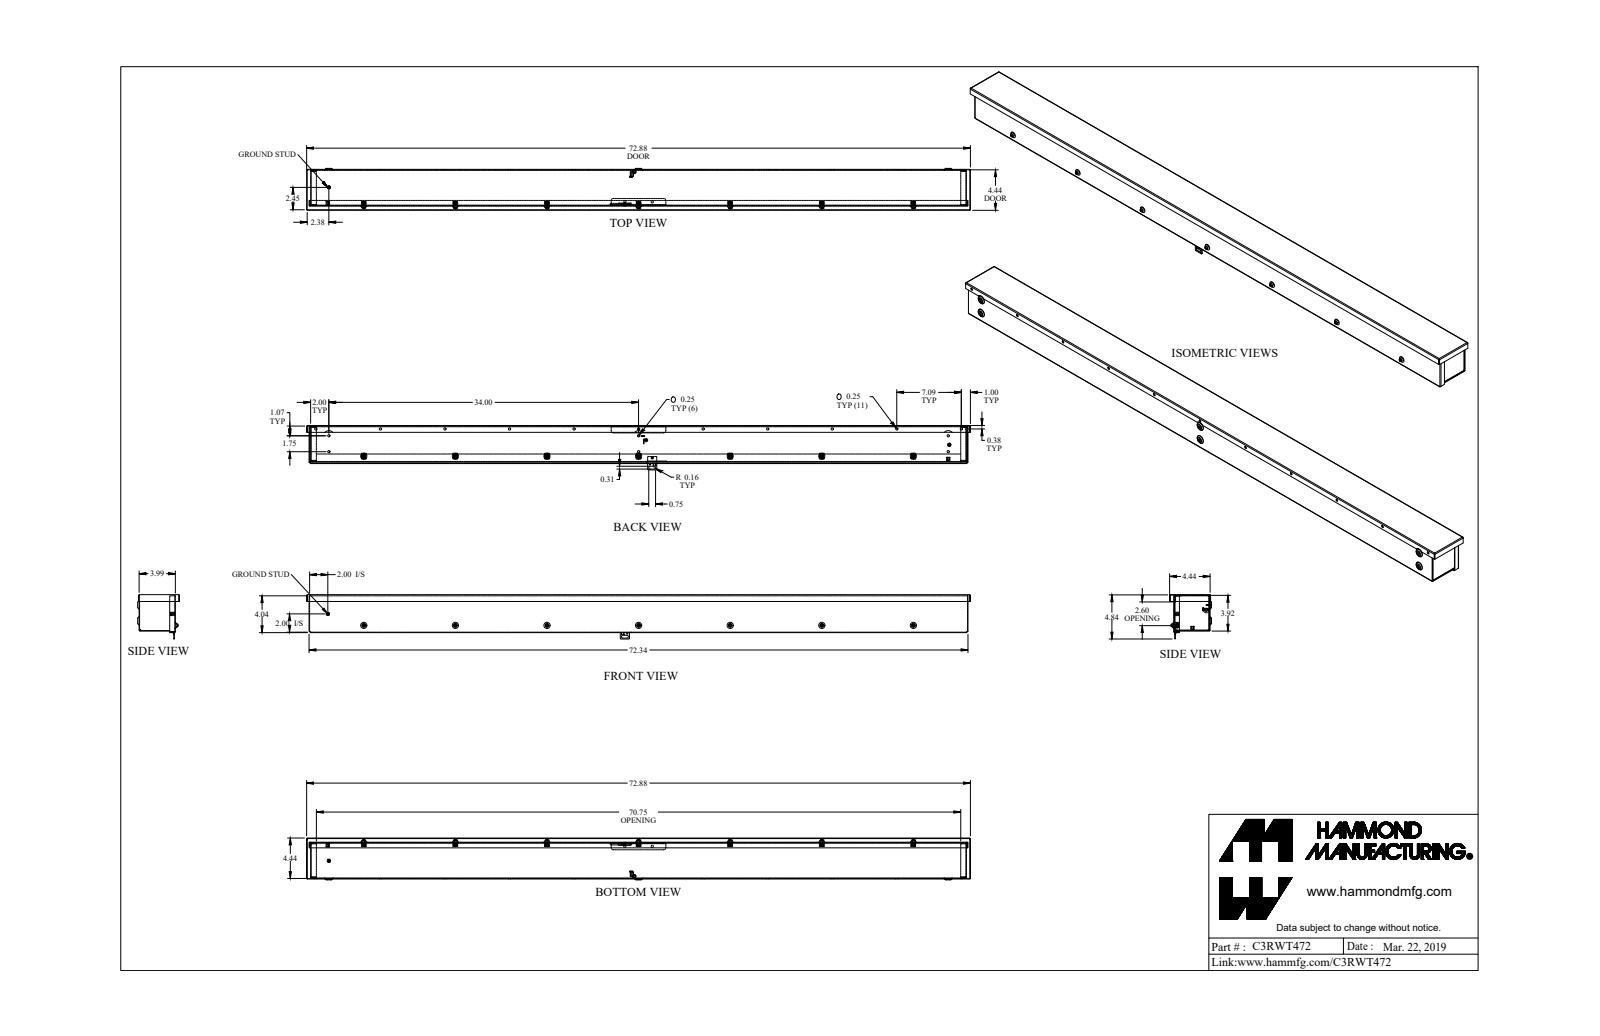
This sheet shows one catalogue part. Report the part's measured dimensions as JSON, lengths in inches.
{"part_name": "C3RWT472_Default", "step_written_by": "SolidWorks 2019 (CONFIG_CONTROL_DESIGN)", "units": "inches", "bodies": {"solids": 35, "faces": 1323, "planar": 712, "cylindrical": 423, "other": 188}, "overall_size": [72.875, 4.871, 4.594], "volume_in3": 82.77, "surface_area_in2": 2939, "round_holes": [[0.25, 19], [0.156, 9], [0.214, 7], [0.23, 7], [0.203, 2], [0.125, 1], [0.137, 1], [0.2, 1], [0.215, 1]], "round_bosses_or_shafts": [[0.19, 8], [0.148, 7], [0.375, 2], [0.5, 1], [0.367, 1], [0.21, 1], [0.152, 1], [0.125, 1]], "partial_cylinders_radius": [[0.08, 28], [0.108, 28], [0.125, 17], [0.022, 14], [0.029, 14], [0.086, 14], [0.171, 7], [0.206, 7]], "face_to_face_distances": [0.057, 3.928, 0.057, 3.871, 3.985, 3.886, 3.943, 4, 3.943, 0.114], "hole_center_spacings": [7.087, 21.263, 28.35, 14.175, 10.057, 14.175, 20.115, 30.172]}
